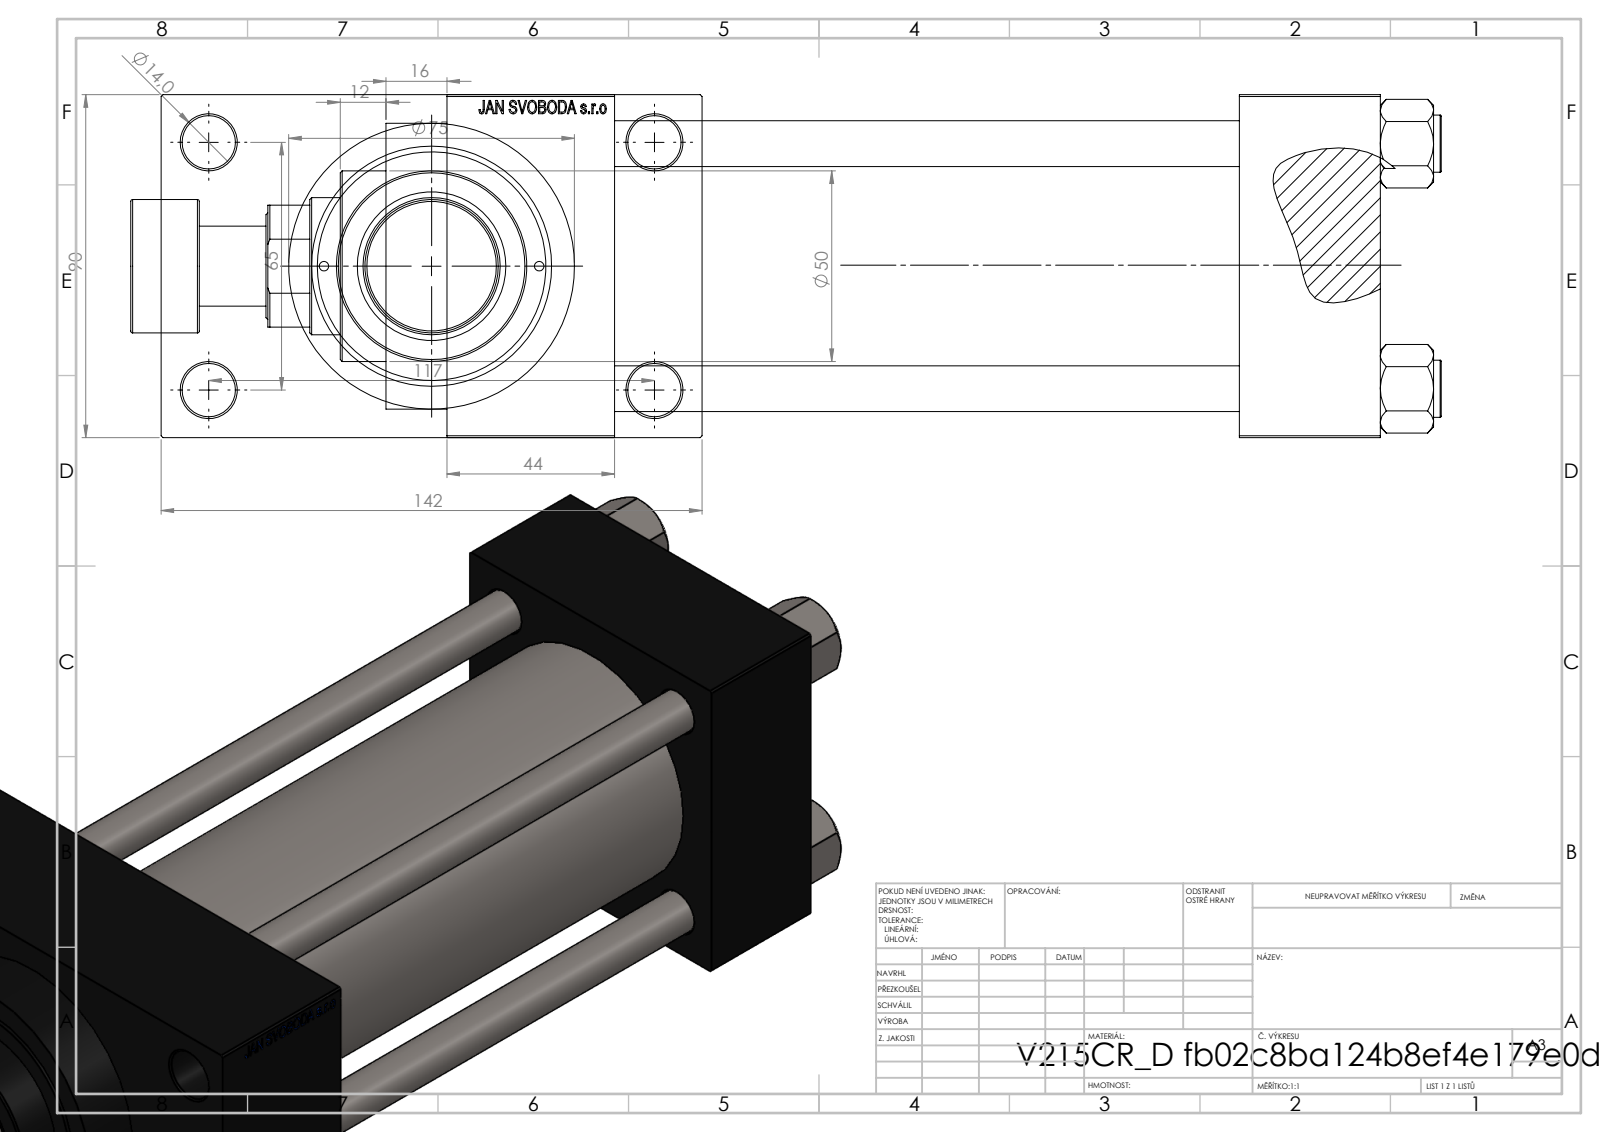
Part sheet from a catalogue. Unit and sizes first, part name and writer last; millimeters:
Units: millimetres
Overall size (bounding box): 344 × 142 × 90
Round holes (diameter × count): ⌀12 ×4, ⌀14 ×4, ⌀2.5 ×2, ⌀7 ×2, ⌀20.96 ×2, ⌀30 ×2, ⌀25.5 ×1, ⌀36 ×1, ⌀39 ×1, ⌀50 ×1, ⌀60 ×1, ⌀63 ×1
Round bosses / shafts (diameter × count): ⌀15 ×4, ⌀75 ×1, ⌀69 ×1, ⌀35 ×1, ⌀21 ×1
Main face-to-face distances: 90, 164, 37, 201, 245, 208, 44, 26, 116, 142
Hole centre spacings: 26.35, 32.39, 44.4, 45.47, 64.3, 66.92, 68.42, 69.81
Volume: 1 355 000 mm³ · Surface area: 282 518 mm²
Bodies: 12 solids, 1125 faces (503 planar, 96 cylindrical, 526 other)
Part name (STEP PRODUCT): V215CR_VCP_D; V215CR_D_TYCINKA; V215_VC_A; NUT_M5_D (+2 more)
STEP written by: SolidWorks 2019 (CONFIG_CONTROL_DESIGN)
